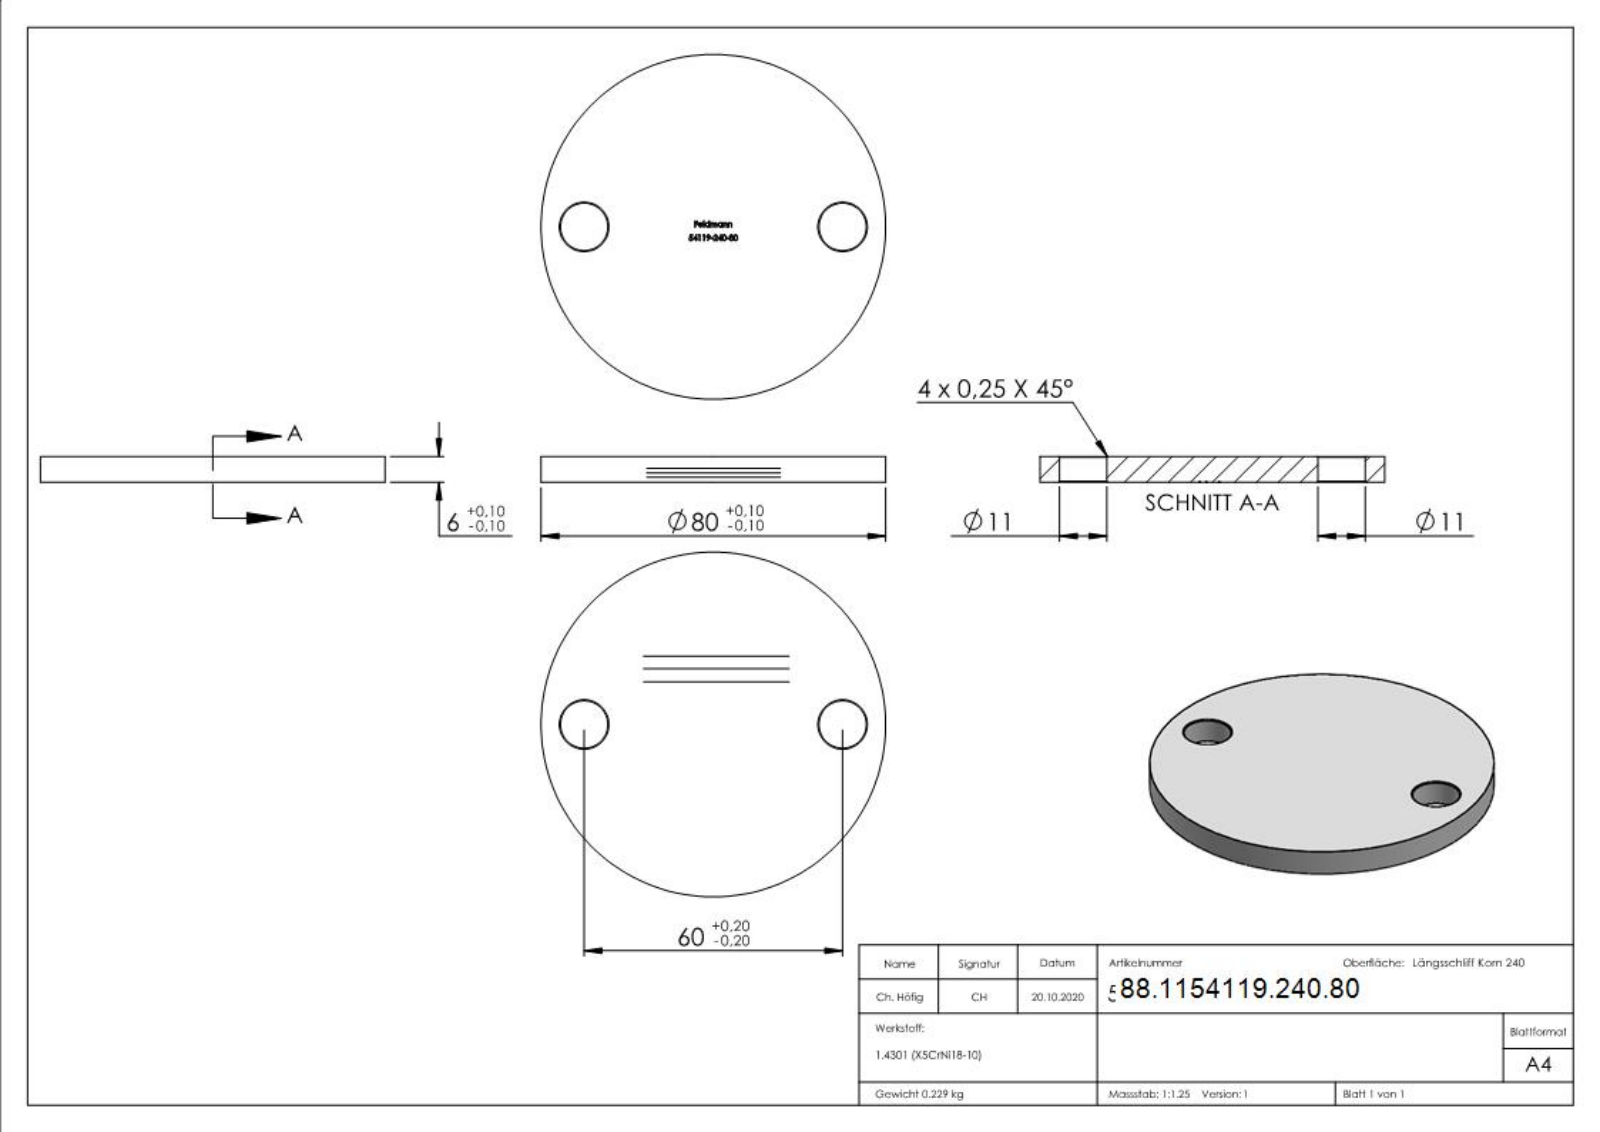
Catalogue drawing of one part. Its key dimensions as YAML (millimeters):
part_name: "54119-240-80"
step_written_by: "SolidWorks 2018 (CONFIG_CONTROL_DESIGN)"
units: millimeters
bodies: {solids: 1, faces: 267, planar: 147, cylindrical: 6, other: 114}
overall_size: [80, 80, 6]
volume: 29014
surface_area: 11586
round_holes:
  - {diameter: 11, count: 2}
round_bosses_or_shafts:
  - {diameter: 80, count: 1}
face_to_face_distances: [6, 5.9, 1.02, 1.19, 2.32, 2.2, 3.19, 2.59, 2.97, 4.07]
hole_center_spacings: [60]
